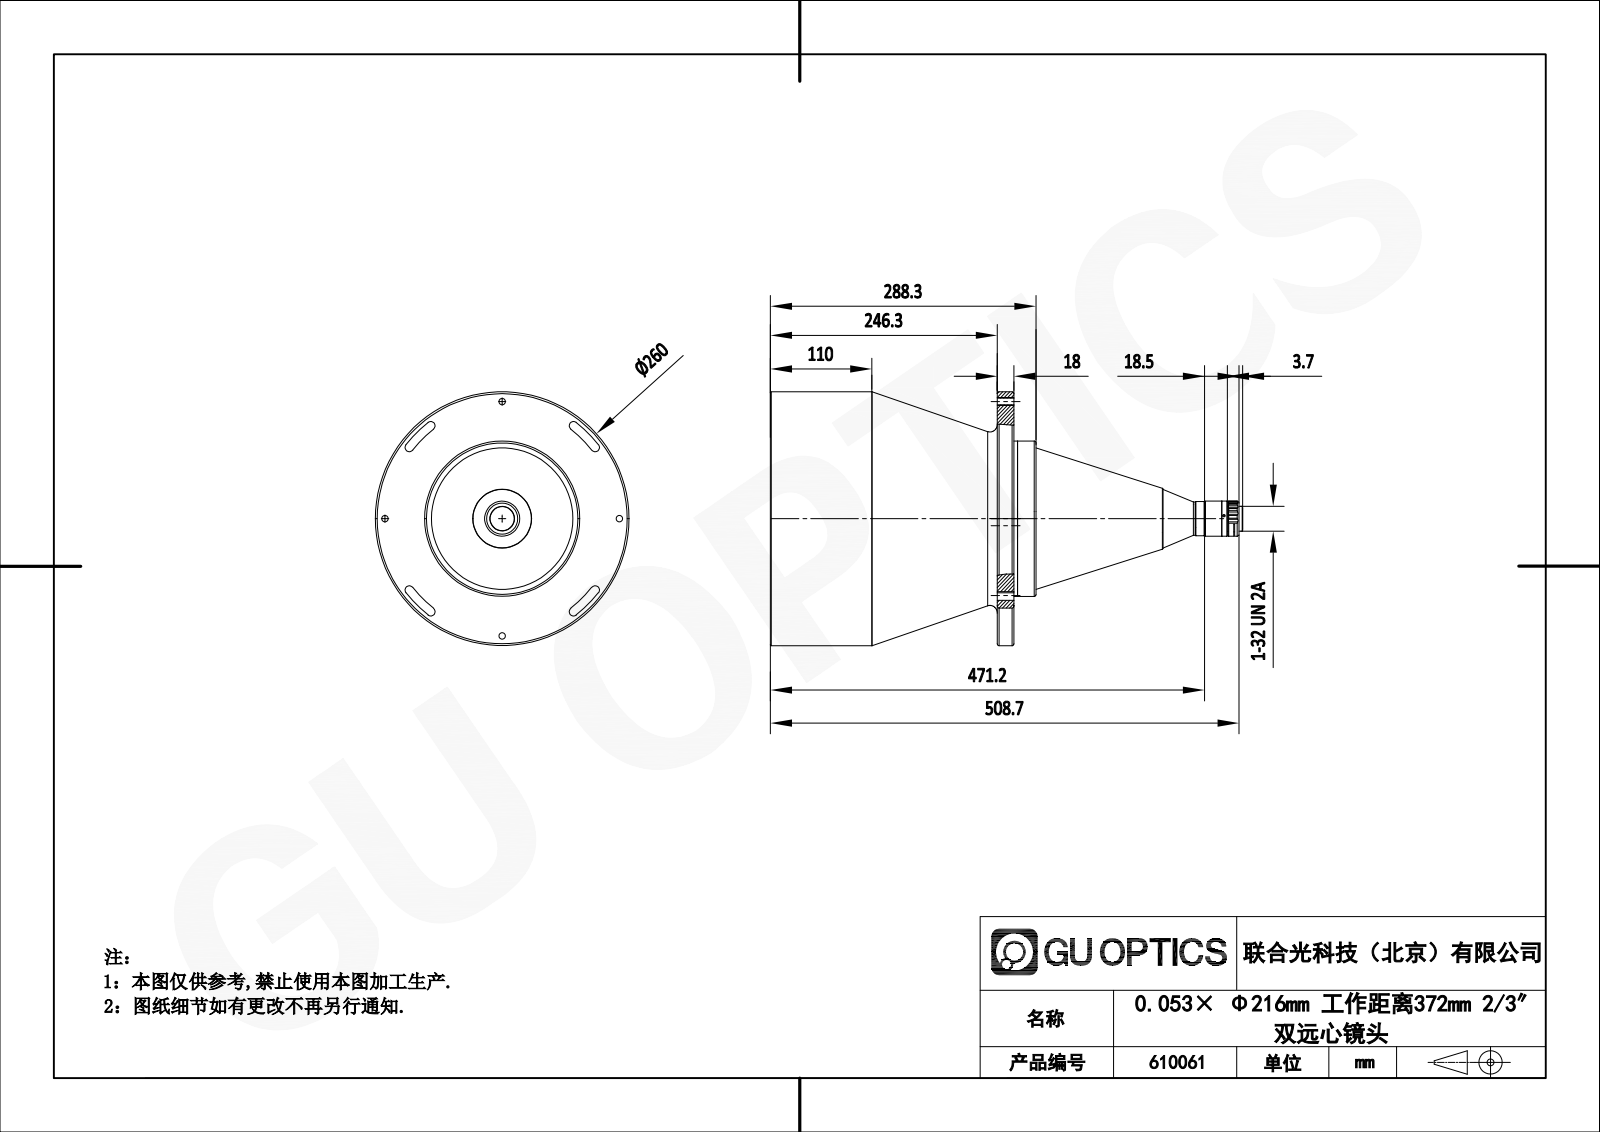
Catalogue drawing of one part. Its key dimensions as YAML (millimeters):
part_name: "DTCM230-216-AL"
step_written_by: "SolidWorks 2017 (CONFIG_CONTROL_DESIGN)"
units: millimeters
bodies: {solids: 1, faces: 100, planar: 8, cylindrical: 54, other: 38}
overall_size: [512.4, 260, 260]
volume: 13630000
surface_area: 391924
round_holes:
  - {diameter: 6.8, count: 4}
  - {diameter: 2.5, count: 3}
round_bosses_or_shafts:
  - {diameter: 260, count: 1}
  - {diameter: 159, count: 1}
  - {diameter: 36, count: 1}
  - {diameter: 35, count: 1}
  - {diameter: 34, count: 1}
  - {diameter: 29, count: 1}
  - {diameter: 25.4, count: 1}
partial_cylinders:
  - {radius: 4.5, count: 8}
  - {radius: 115.5, count: 1}
  - {radius: 124.5, count: 1}
face_to_face_distances: [264.3, 246.3, 18, 288.3, 42, 24, 512.4, 266.1, 248.1, 224.1]
hole_center_spacings: [169.71, 240]
